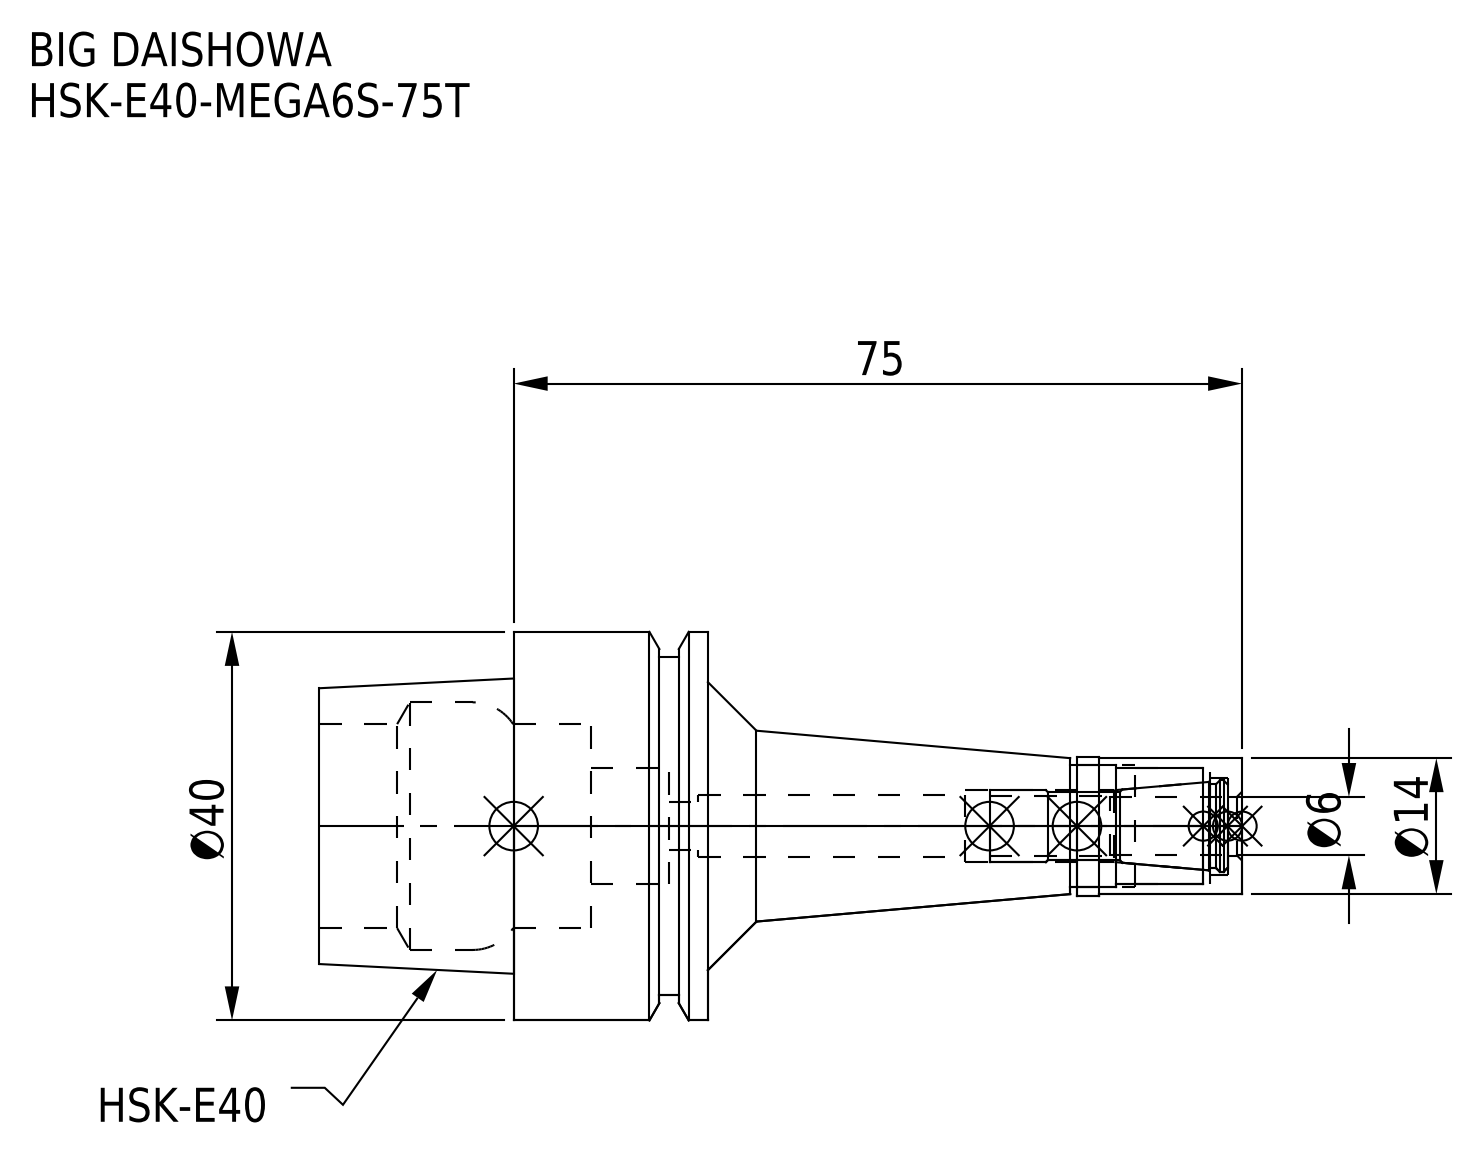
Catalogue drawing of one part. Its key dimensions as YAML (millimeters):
part_name: "HSK-E40-MEGA6S-75T-060-FreeParts; HSK-E40-MEGA6S-75T; DXF_TEMP_ASSY_ASM_4_ASM.stp; HSK-E40-MEGA6S-75T_1.stp (+3 more)"
step_written_by: "SolidWorks 2019 (CONFIG_CONTROL_DESIGN)"
units: millimeters
bodies: {solids: 2, faces: 74, planar: 18, cylindrical: 38, other: 18}
overall_size: [95, 40, 40]
volume: 35669
surface_area: 14610
round_holes:
  - {diameter: 5, count: 1}
  - {diameter: 6.1, count: 1}
  - {diameter: 6.4, count: 1}
  - {diameter: 7.4, count: 1}
  - {diameter: 10, count: 1}
  - {diameter: 12, count: 1}
  - {diameter: 12.5, count: 1}
  - {diameter: 21, count: 1}
  - {diameter: 25.5, count: 1}
round_bosses_or_shafts:
  - {diameter: 40, count: 1}
  - {diameter: 34.8, count: 1}
  - {diameter: 14.3, count: 1}
  - {diameter: 14, count: 1}
face_to_face_distances: [20, 40, 12.05, 7.95, 27.95, 17, 58, 2, 55, 67.05]
